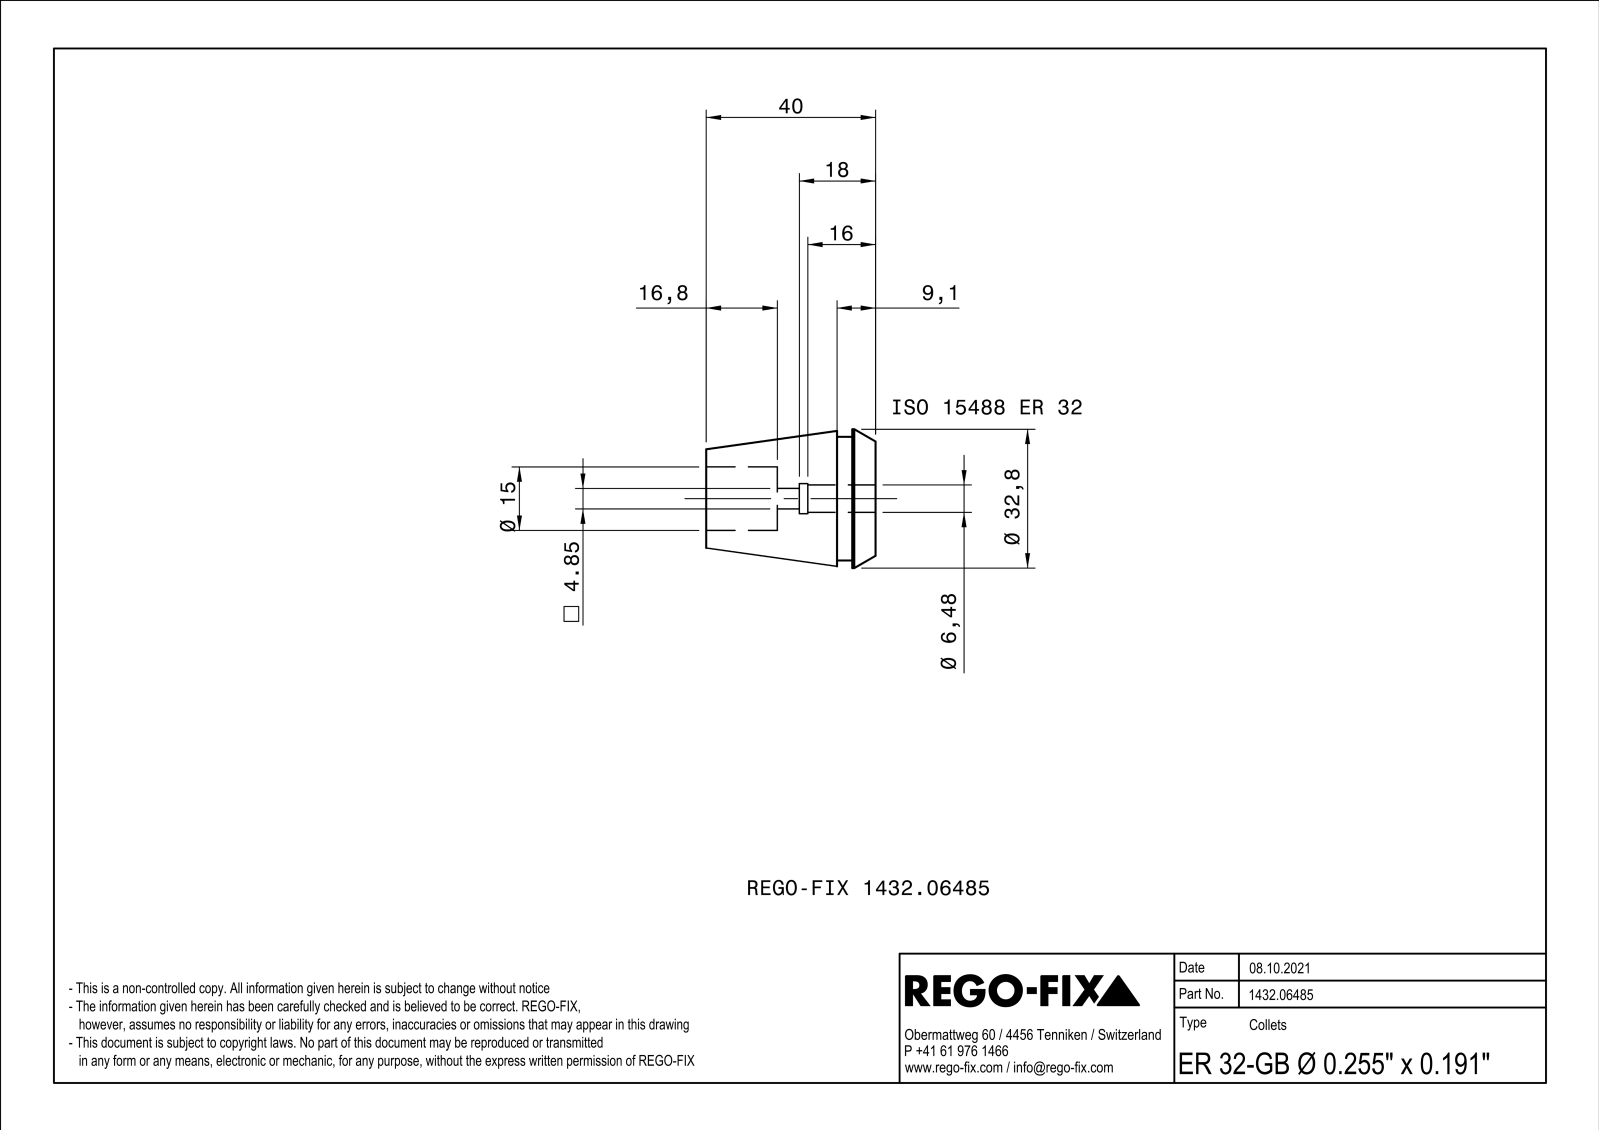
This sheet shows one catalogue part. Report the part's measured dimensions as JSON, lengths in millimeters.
{"part_name": "NOCUT", "step_written_by": "SIEMENS PLM Software Solid Edge ST10 (AUTOMOTIVE_DESIGN)", "units": "millimeters", "bodies": {"solids": 1, "faces": 176, "planar": 68, "cylindrical": 40, "other": 68}, "overall_size": [40, 32.79, 32.79], "volume_mm3": 19272, "surface_area_mm2": 10715, "round_holes": [[6.48, 1], [15, 1]], "round_bosses_or_shafts": [[32.8, 1], [29.2, 1]], "partial_cylinders_radius": [[2.85, 1], [3.4, 1], [3.55, 1]], "face_to_face_distances": [0.8, 40, 5.5, 34.5, 23.2, 17.7, 16.8, 3.1, 9.1, 3.6]}
